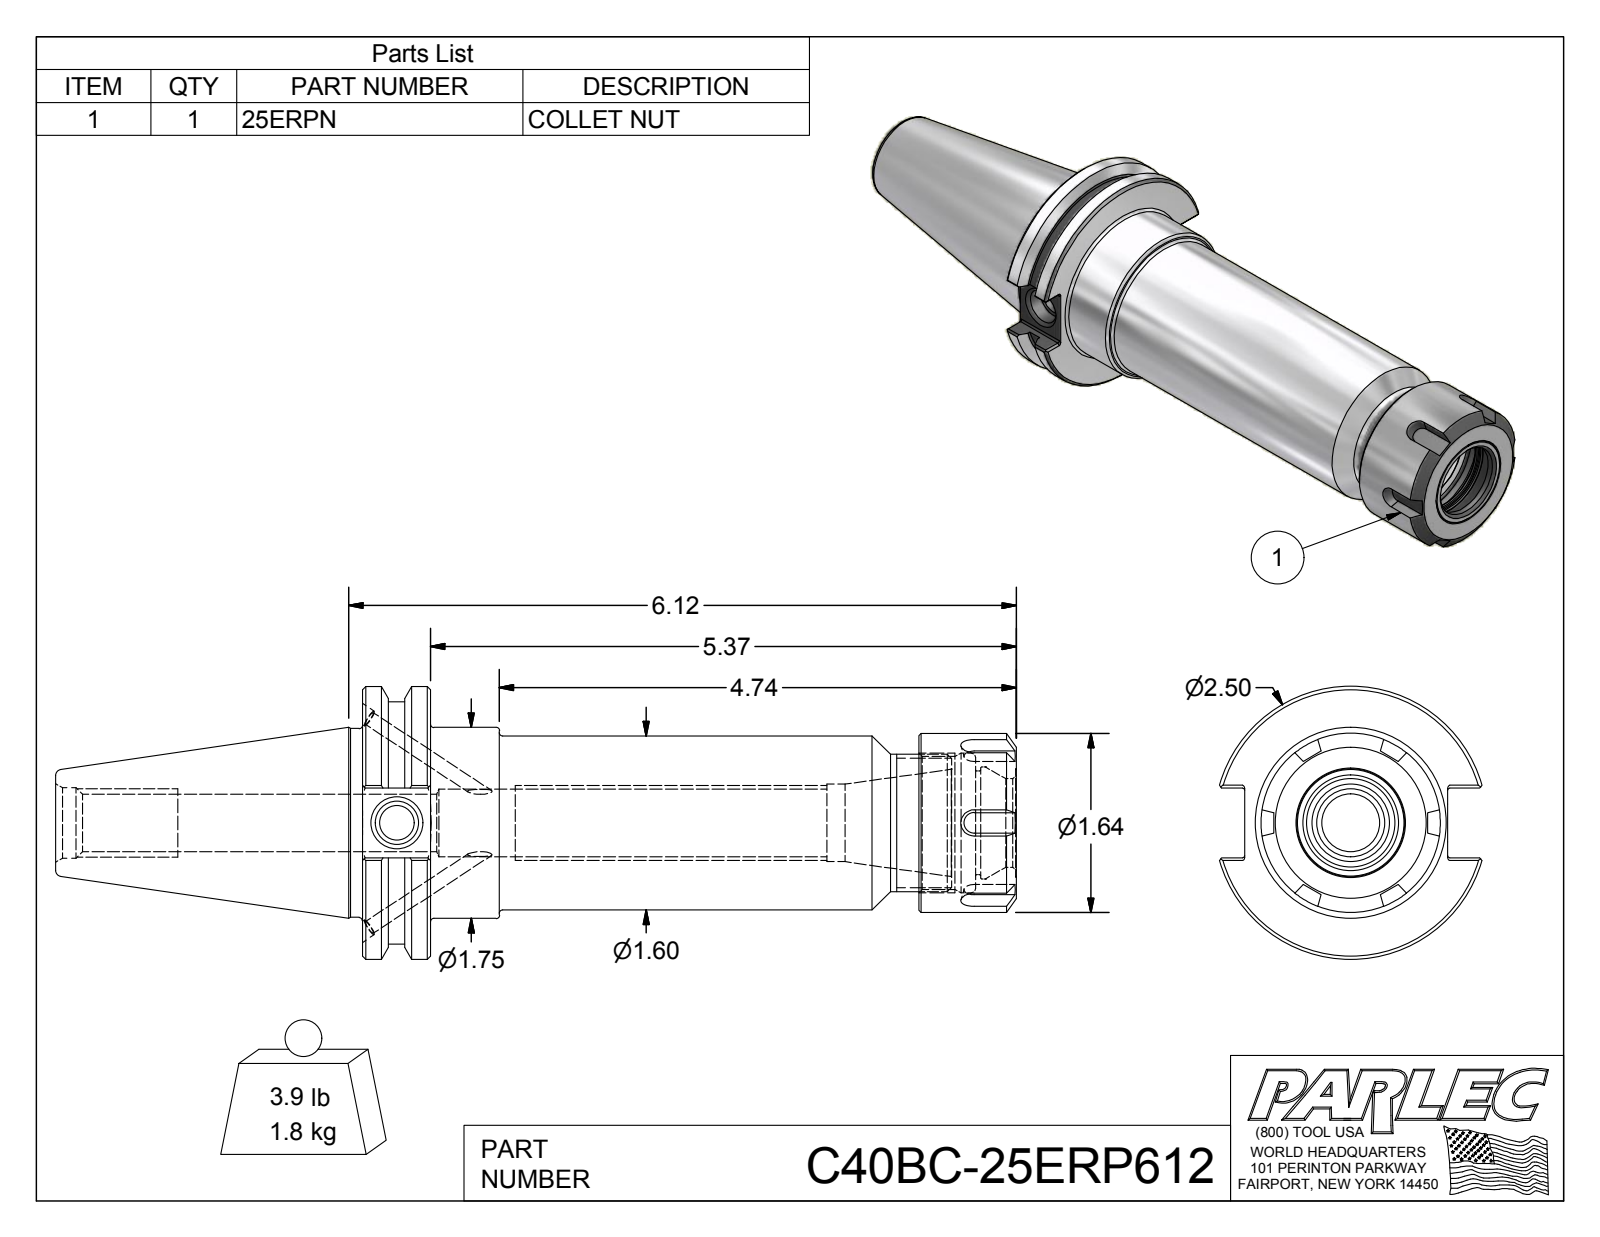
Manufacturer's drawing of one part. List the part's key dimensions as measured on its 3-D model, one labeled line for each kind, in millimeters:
Part name (STEP PRODUCT): 25ERPN; C40BC-25ER6-1; 029-965; C40BC-25ERP612
STEP written by: Autodesk Inventor 2016 (AUTOMOTIVE_DESIGN)
Units: millimetres
Bodies: 4 solids, 171 faces (78 planar, 44 cylindrical, 49 other)
Overall size (bounding box): 223.71 × 63.5 × 61.05
Volume: 239 702 mm³ · Surface area: 49 037 mm²
Round holes (diameter × count): ⌀3.3 ×2, ⌀4.1 ×2, ⌀8 ×1, ⌀10.13 ×1, ⌀13.39 ×1, ⌀15.75 ×1, ⌀16.46 ×1, ⌀18.03 ×1, ⌀20.6 ×1, ⌀24.13 ×1, ⌀26.09 ×1, ⌀30.91 ×1
Round bosses / shafts (diameter × count): ⌀4.2 ×2, ⌀4 ×2, ⌀63.5 ×1, ⌀56.36 ×1, ⌀44.45 ×1, ⌀43.94 ×1, ⌀41.73 ×1, ⌀40.51 ×1
Partial cylindrical surfaces — rounded edges, fillets, slot ends (radius × count): R0.51 ×12
Main face-to-face distances: 15.87, 152.27, 136.4, 129.59, 113.72, 22.68, 142.74, 126.87, 13.15, 9.53
